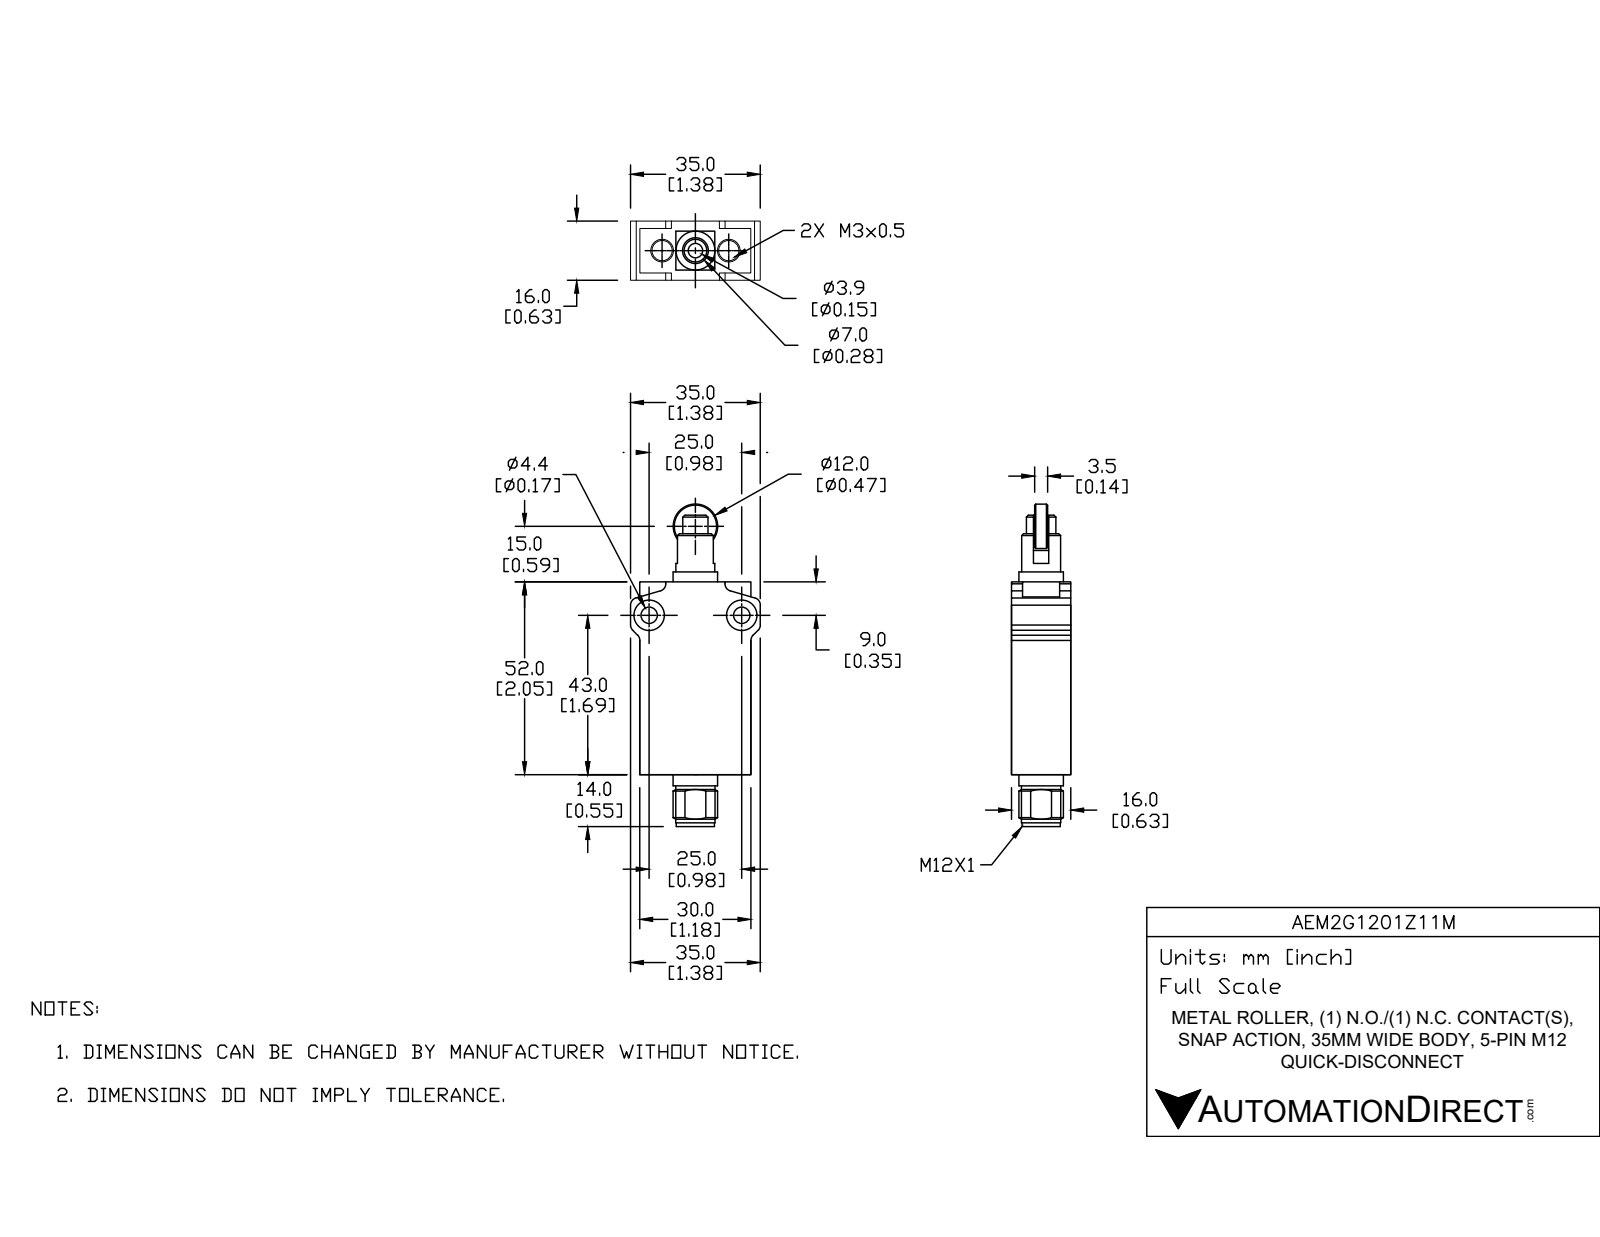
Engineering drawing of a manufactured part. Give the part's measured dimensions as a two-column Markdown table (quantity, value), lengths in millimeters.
| quantity | value |
| --- | --- |
| part name | AEM2G1201Z11M |
| STEP written by | SolidWorks 2017 (AUTOMOTIVE_DESIGN) |
| units | millimeters |
| bodies | 4 solids, 180 faces (67 planar, 72 cylindrical, 41 other) |
| overall size | 87 × 35 × 16 |
| volume | 26 920 mm³ |
| surface area | 9 413 mm² |
| round holes (diameter × count) | 3 × 2, 4.4 × 2, 8.2 × 2, 8.1 × 1 |
| round bosses / shafts (diameter × count) | 12 × 2, 10.6 × 1, 10.5 × 1, 10.3 × 1, 8 × 1, 5.6 × 1 |
| partial cylindrical surfaces (radius × count) | 2 × 8, 6.5 × 1 |
| main face-to-face distances | 16, 30, 52, 12, 47.2, 4.8, 5.9, 3.8, 4, 6 |
| hole center spacings | 9.5, 19, 25 |
